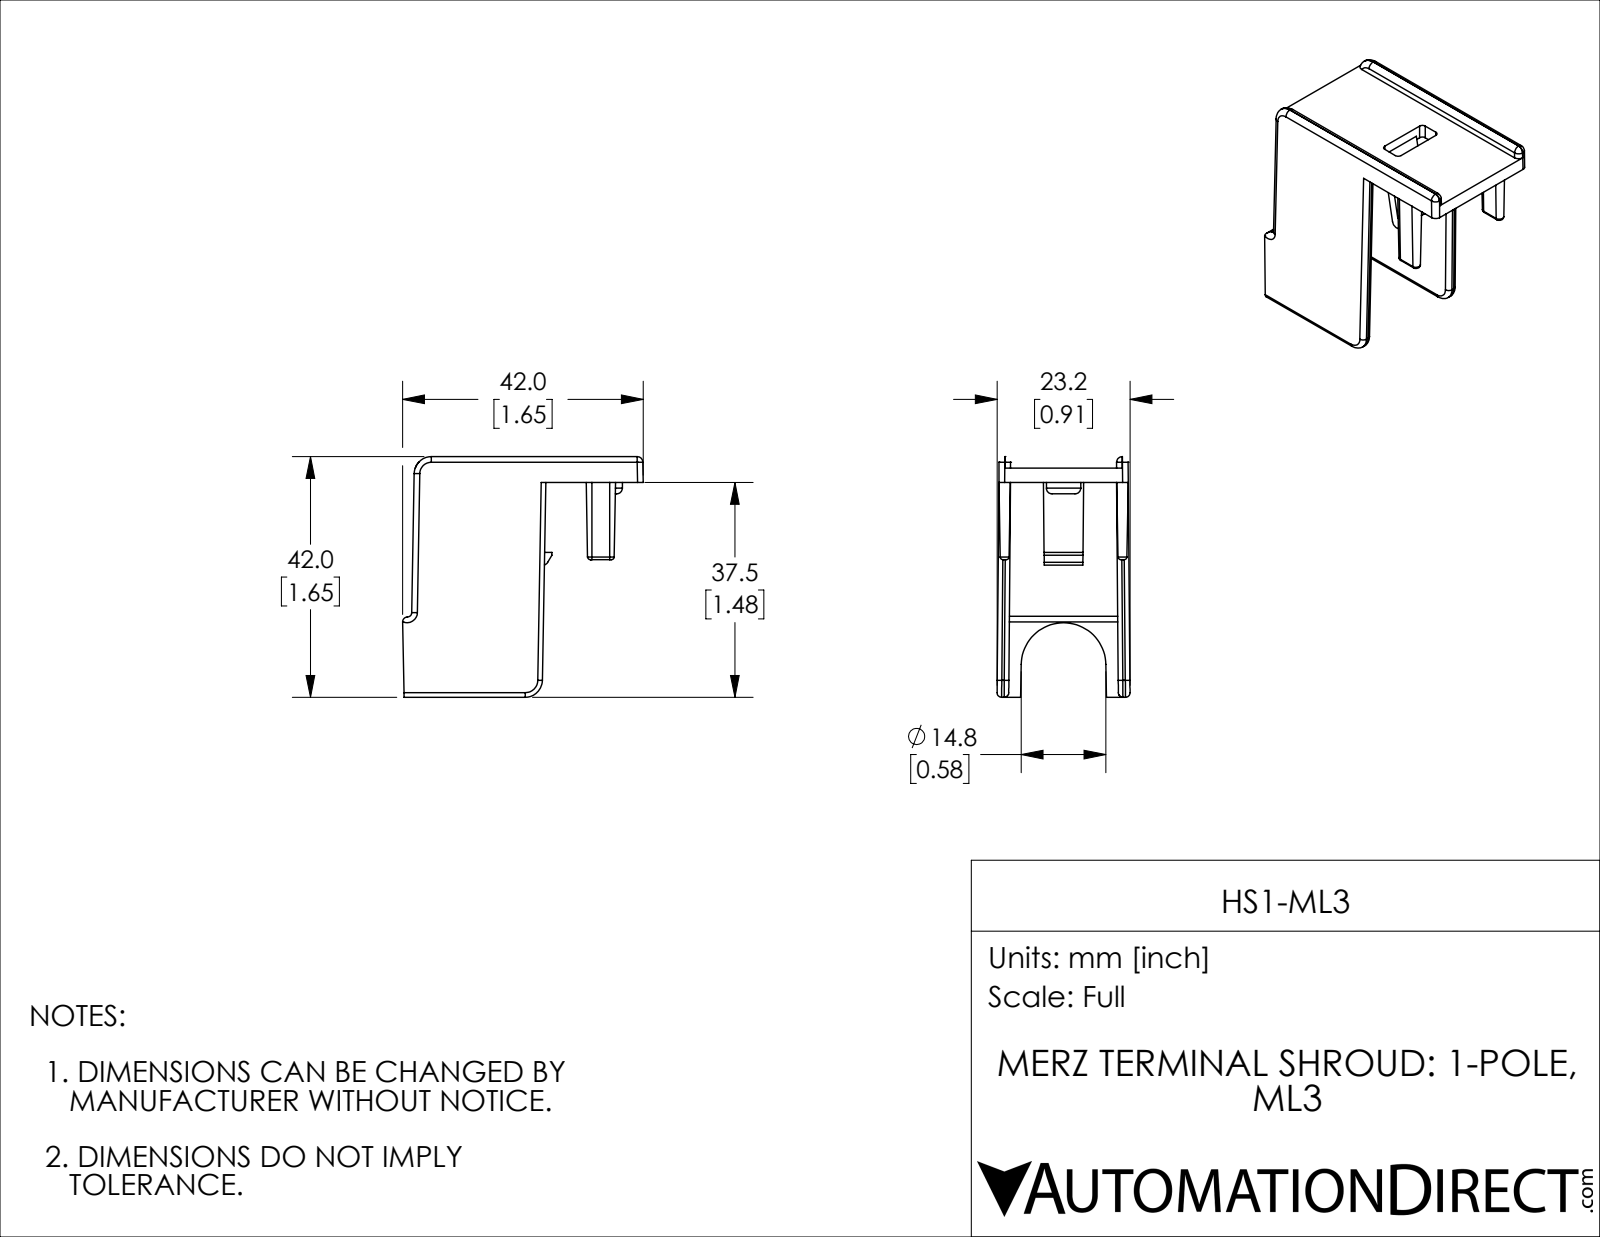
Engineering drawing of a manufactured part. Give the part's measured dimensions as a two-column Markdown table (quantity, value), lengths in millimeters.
| quantity | value |
| --- | --- |
| part name | HS1-ML3 |
| STEP written by | SolidWorks 2019 (AUTOMOTIVE_DESIGN) |
| units | millimeters |
| bodies | 1 solid, 111 faces (44 planar, 40 cylindrical, 27 other) |
| overall size | 42 × 42 × 23.2 |
| volume | 7 780 mm³ |
| surface area | 7 658 mm² |
| round bosses / shafts (diameter × count) | 6 × 1 |
| partial cylindrical surfaces (radius × count) | 0.8 × 10, 1 × 10, 0.5 × 4, 0.7 × 4, 1 × 3, 3 × 2, 7.4 × 1 |
| main face-to-face distances | 2, 2.5, 1.5, 2, 20.6, 18.5, 2.1, 42.4, 12.8, 14.8 |
